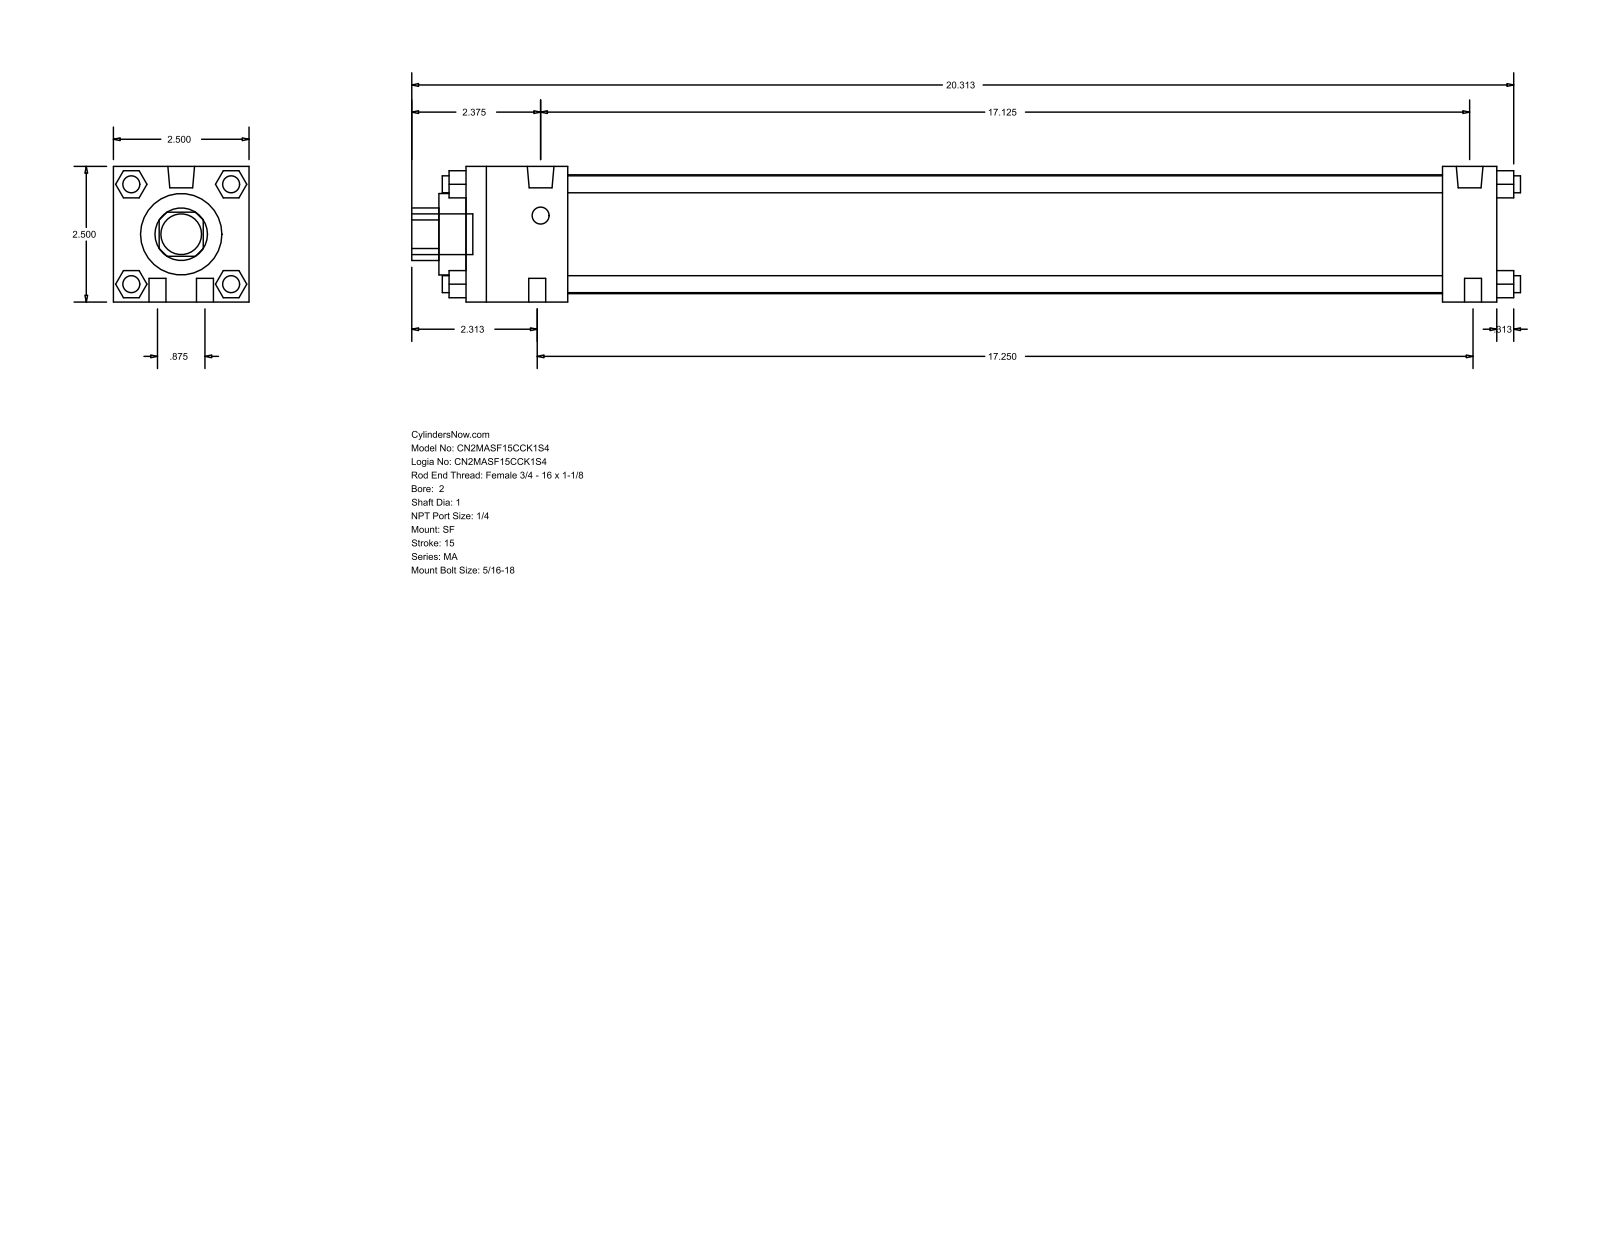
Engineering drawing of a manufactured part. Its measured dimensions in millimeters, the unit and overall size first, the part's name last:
Units: millimetres
Overall size (bounding box): 519.11 × 63.5 × 63.5
Round holes (diameter × count): ⌀25.4 ×1, ⌀38.1 ×1, ⌀55.63 ×1
Round bosses / shafts (diameter × count): ⌀7.94 ×10, ⌀12.49 ×2, ⌀19.05 ×1
Partial cylindrical surfaces — rounded edges, fillets, slot ends (radius × count): R12.29 ×1
Main face-to-face distances: 63.5, 482.6, 12.7, 25.4, 457.2, 47.63, 409.57, 434.97, 40.47, 23.37
Bodies: 0 solids, 124 faces (94 planar, 30 cylindrical, 0 other)
Part name (STEP PRODUCT): MA_SF__0200_1
STEP written by: GSSL Pune (CONFIG_CONTROL_DESIGN)
